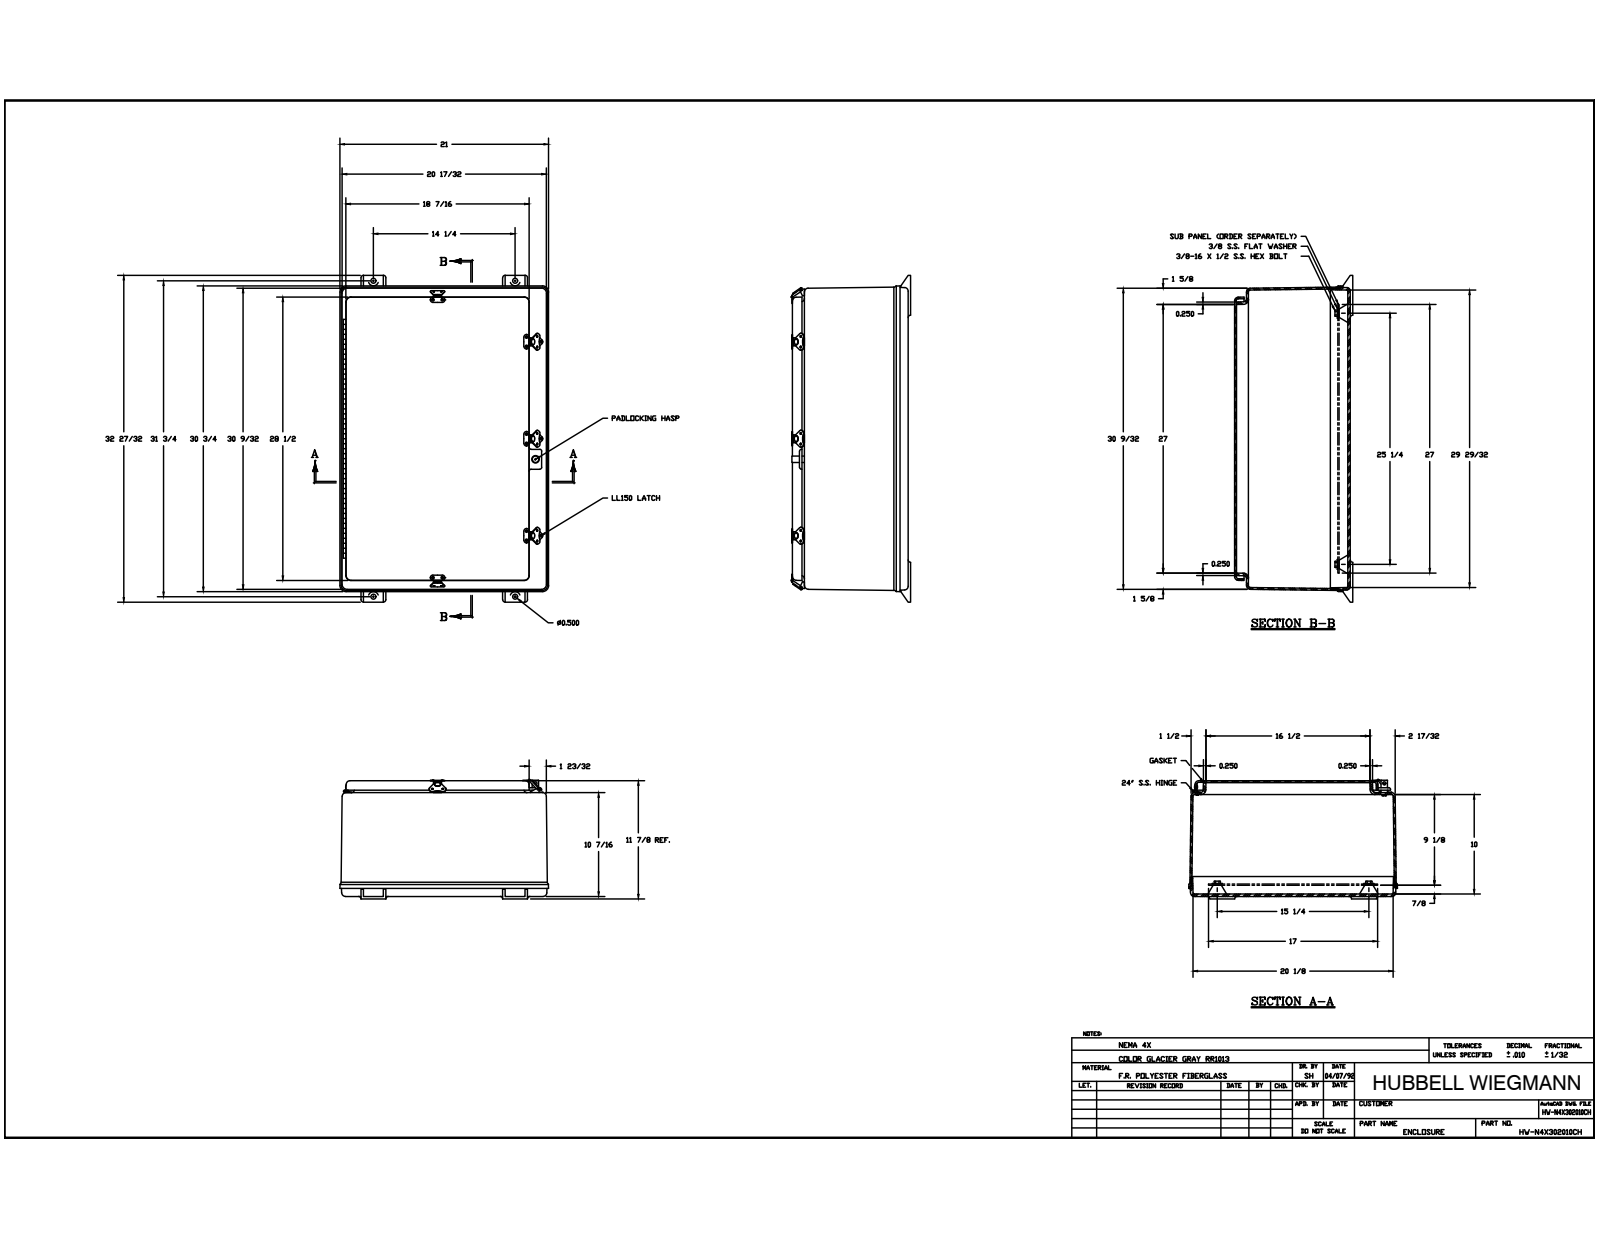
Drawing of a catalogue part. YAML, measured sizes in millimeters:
part_name: "WPN302010SHWT; WPN3020B; WPN302010HWTPCVR; N302010G (+8 more)"
step_written_by: "Autodesk Inventor 2014 (AUTOMOTIVE_DESIGN)"
units: millimeters
bodies: {solids: 63, faces: 1758, planar: 670, cylindrical: 702, other: 386}
overall_size: [834.23, 533.4, 310.92]
volume: 8530000
surface_area: 3564000
round_holes:
  - {diameter: 3.3, count: 37}
  - {diameter: 1.59, count: 20}
  - {diameter: 3.5, count: 10}
  - {diameter: 4.76, count: 10}
  - {diameter: 1.65, count: 8}
  - {diameter: 14.3, count: 4}
  - {diameter: 3.43, count: 3}
  - {diameter: 3.97, count: 3}
  - {diameter: 12.95, count: 2}
  - {diameter: 12.96, count: 2}
  - {diameter: 3.17, count: 1}
  - {diameter: 5.11, count: 1}
round_bosses_or_shafts:
  - {diameter: 3.56, count: 20}
  - {diameter: 7.54, count: 8}
  - {diameter: 12.7, count: 5}
  - {diameter: 5.08, count: 3}
  - {diameter: 6.35, count: 1}
  - {diameter: 5.11, count: 1}
partial_cylinders:
  - {radius: 0.25, count: 127}
  - {radius: 6.35, count: 24}
  - {radius: 7.94, count: 23}
  - {radius: 4.76, count: 21}
  - {radius: 0.76, count: 20}
  - {radius: 9.53, count: 13}
  - {radius: 12.7, count: 12}
  - {radius: 1.59, count: 10}
face_to_face_distances: [4.76, 6.35, 292.1, 285.75, 3.97, 296.07, 289.72, 265.11, 260.35, 31.75]
hole_center_spacings: [190.5, 393.7, 247.65, 25.4, 203.2, 584.2, 25.82, 81.56]
